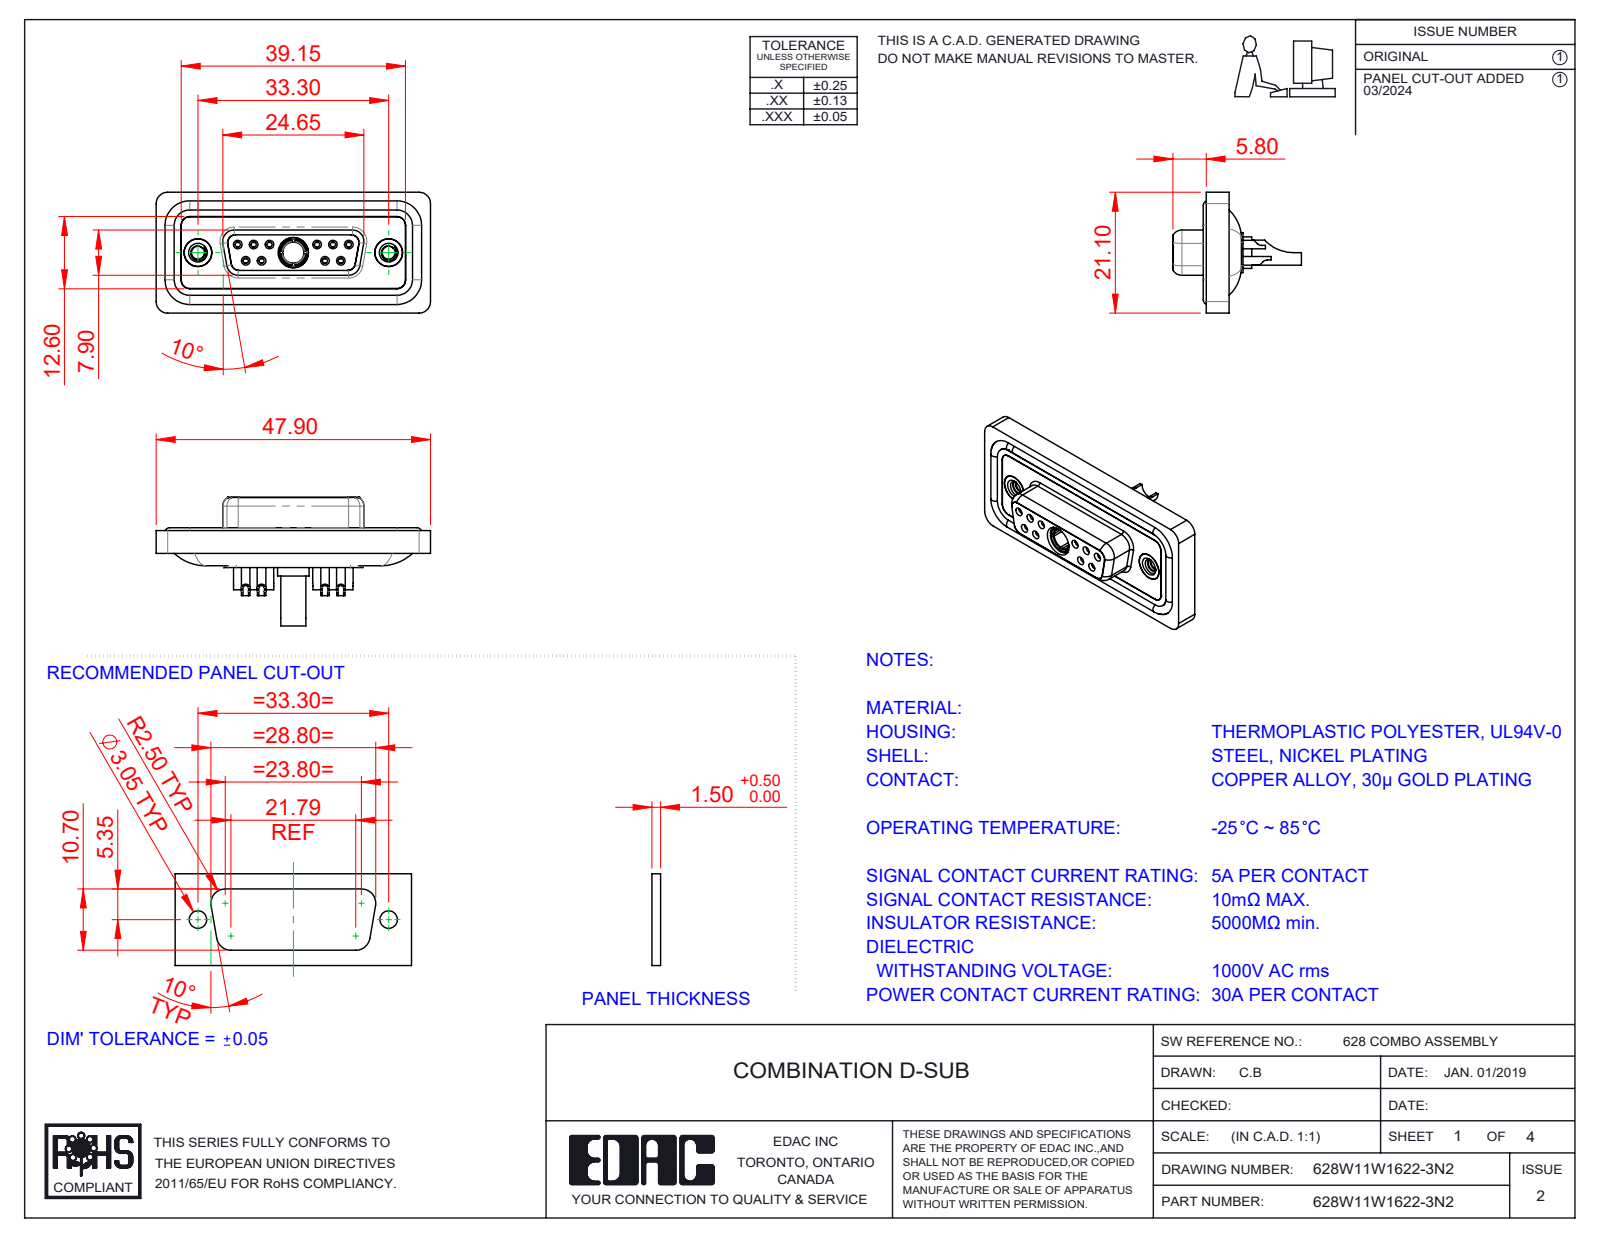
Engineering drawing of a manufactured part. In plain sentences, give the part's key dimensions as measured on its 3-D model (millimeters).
The part is named "628Combo Shell Front_15 Contacts; 628Combo Contact Row 1_22; 628Combo Contact Row 2_22; 628Combo Threaded Rivet_2 (+5 more)". Its 3-D file was written by "SolidWorks 2023 (CONFIG_CONTROL_DESIGN)". It is 19 solids with 1016 faces: 307 planar, 424 cylindrical and 285 other. Overall it measures 47.9 by 22.45 by 21.1 millimeters. Its volume is 6 169 cubic millimeters and its surface area 10 240 square millimeters. Round holes: 10 of diameter 0.9, 10 of diameter 1, 10 of diameter 1.1, 10 of diameter 1.5, 10 of diameter 2, 6 of diameter 1.7, 4 of diameter 1.6, 3 of diameter 4.85, 2 of diameter 2.26, 2 of diameter 4, 2 of diameter 4.05, 2 of diameter 5. Round bosses or shafts: 10 of diameter 2.2, 10 of diameter 1.6, 2 of diameter 4.95, 2 of diameter 4.8, 1 of diameter 5.5, 1 of diameter 5.2, 1 of diameter 4.96, 1 of diameter 4.75. Partial cylindrical surfaces (rounded edges, fillets, slot ends): 22 of radius 1.5, 20 of radius 2, 12 of radius 1.35, 8 of radius 1.6, 6 of radius 1, 4 of radius 0.25, 4 of radius 0.5, 4 of radius 0.6. The main face-to-face distances are 0.4, 1.6, 1.8, 2.9, 0.5, 1.1, 5.65, 7.45, 6.6, 7.05. The hole center spacings are 3.16, 2.77, 13.85, 11.08, 16.62, 5.03, 5.04, 5.54.
